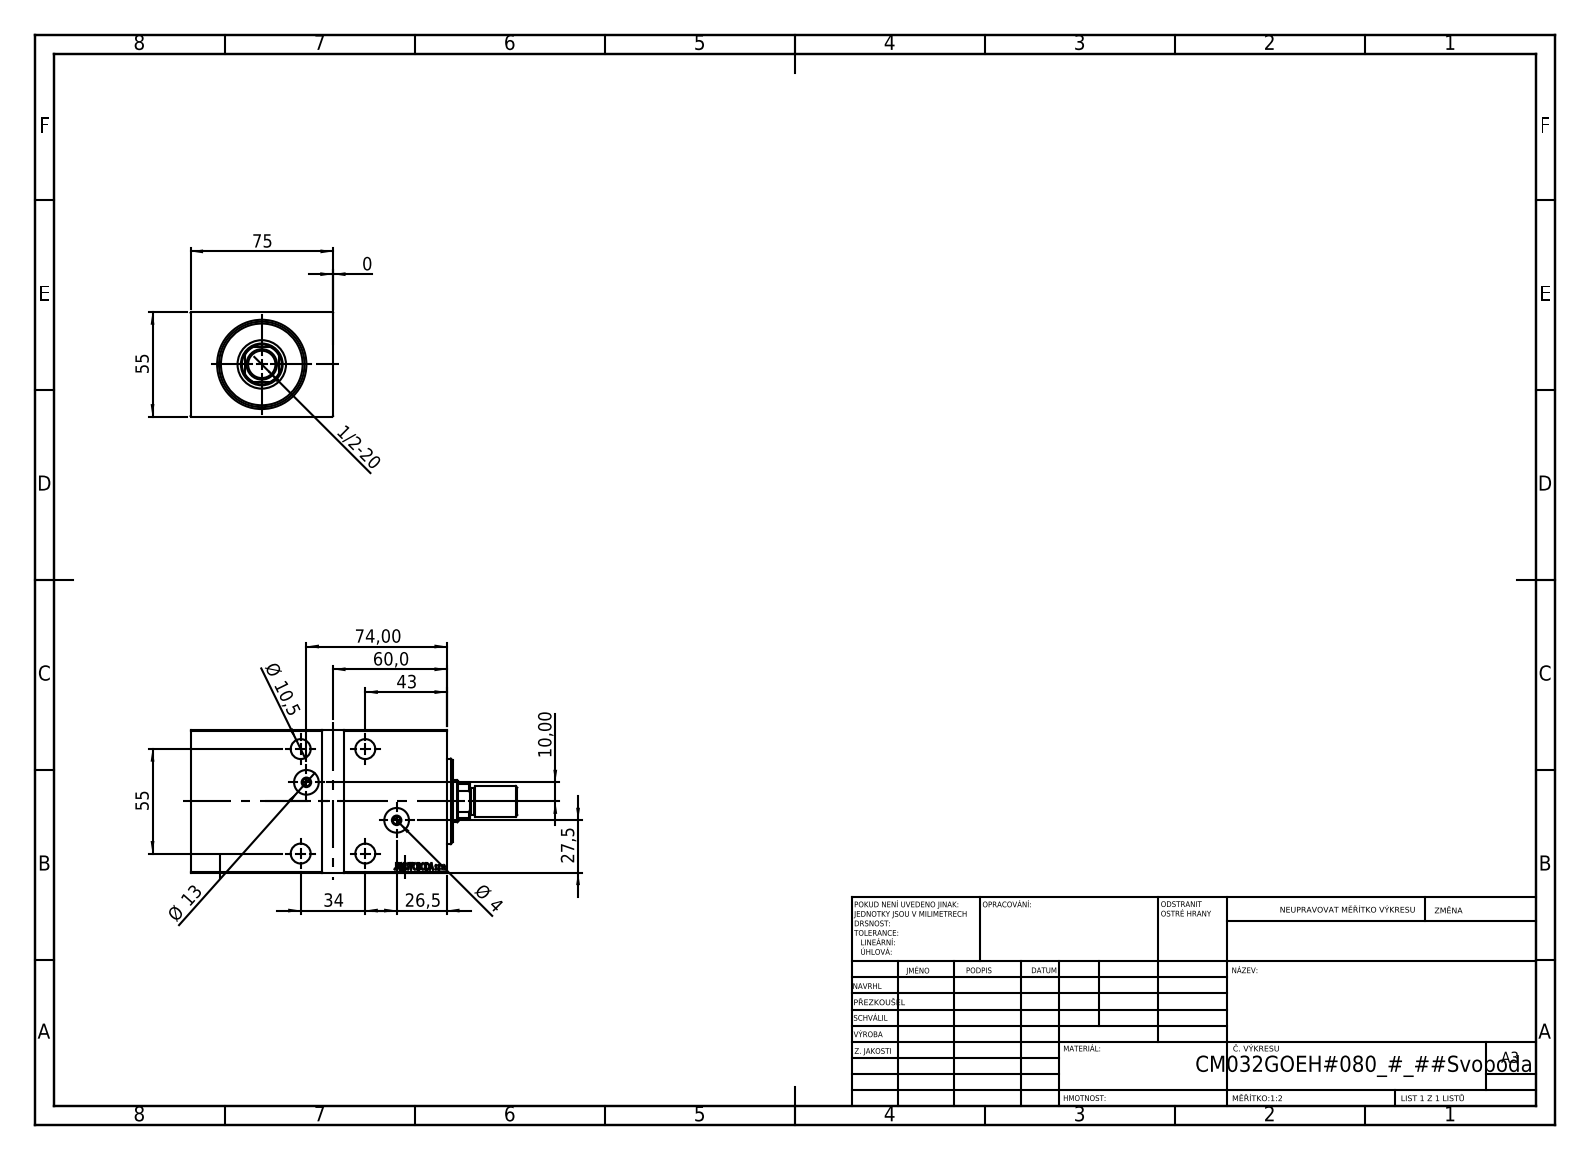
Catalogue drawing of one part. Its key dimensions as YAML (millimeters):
part_name: "Zatka_OIL_PORT; V450CM_G_Body; V450CM_G_VCP; V450CM_VC_G (+1 more)"
step_written_by: "SolidWorks 2019 (CONFIG_CONTROL_DESIGN)"
units: millimeters
bodies: {solids: 6, faces: 909, planar: 445, cylindrical: 60, other: 404}
overall_size: [172, 75, 55]
volume: 503600
surface_area: 85458
round_holes:
  - {diameter: 10.5, count: 5}
  - {diameter: 16.5, count: 4}
  - {diameter: 4, count: 2}
  - {diameter: 13, count: 2}
  - {diameter: 22, count: 1}
  - {diameter: 25.5, count: 1}
  - {diameter: 32, count: 1}
  - {diameter: 34, count: 1}
  - {diameter: 45, count: 1}
round_bosses_or_shafts:
  - {diameter: 18, count: 2}
  - {diameter: 5, count: 2}
  - {diameter: 27, count: 1}
  - {diameter: 16, count: 1}
  - {diameter: 14, count: 1}
partial_cylinders:
  - {radius: 10.5, count: 1}
face_to_face_distances: [55, 75, 135, 5, 3, 130, 125, 10, 120, 138]
hole_center_spacings: [34, 55, 64.66, 17.76, 24.05, 35.6, 37.62, 40.97]
